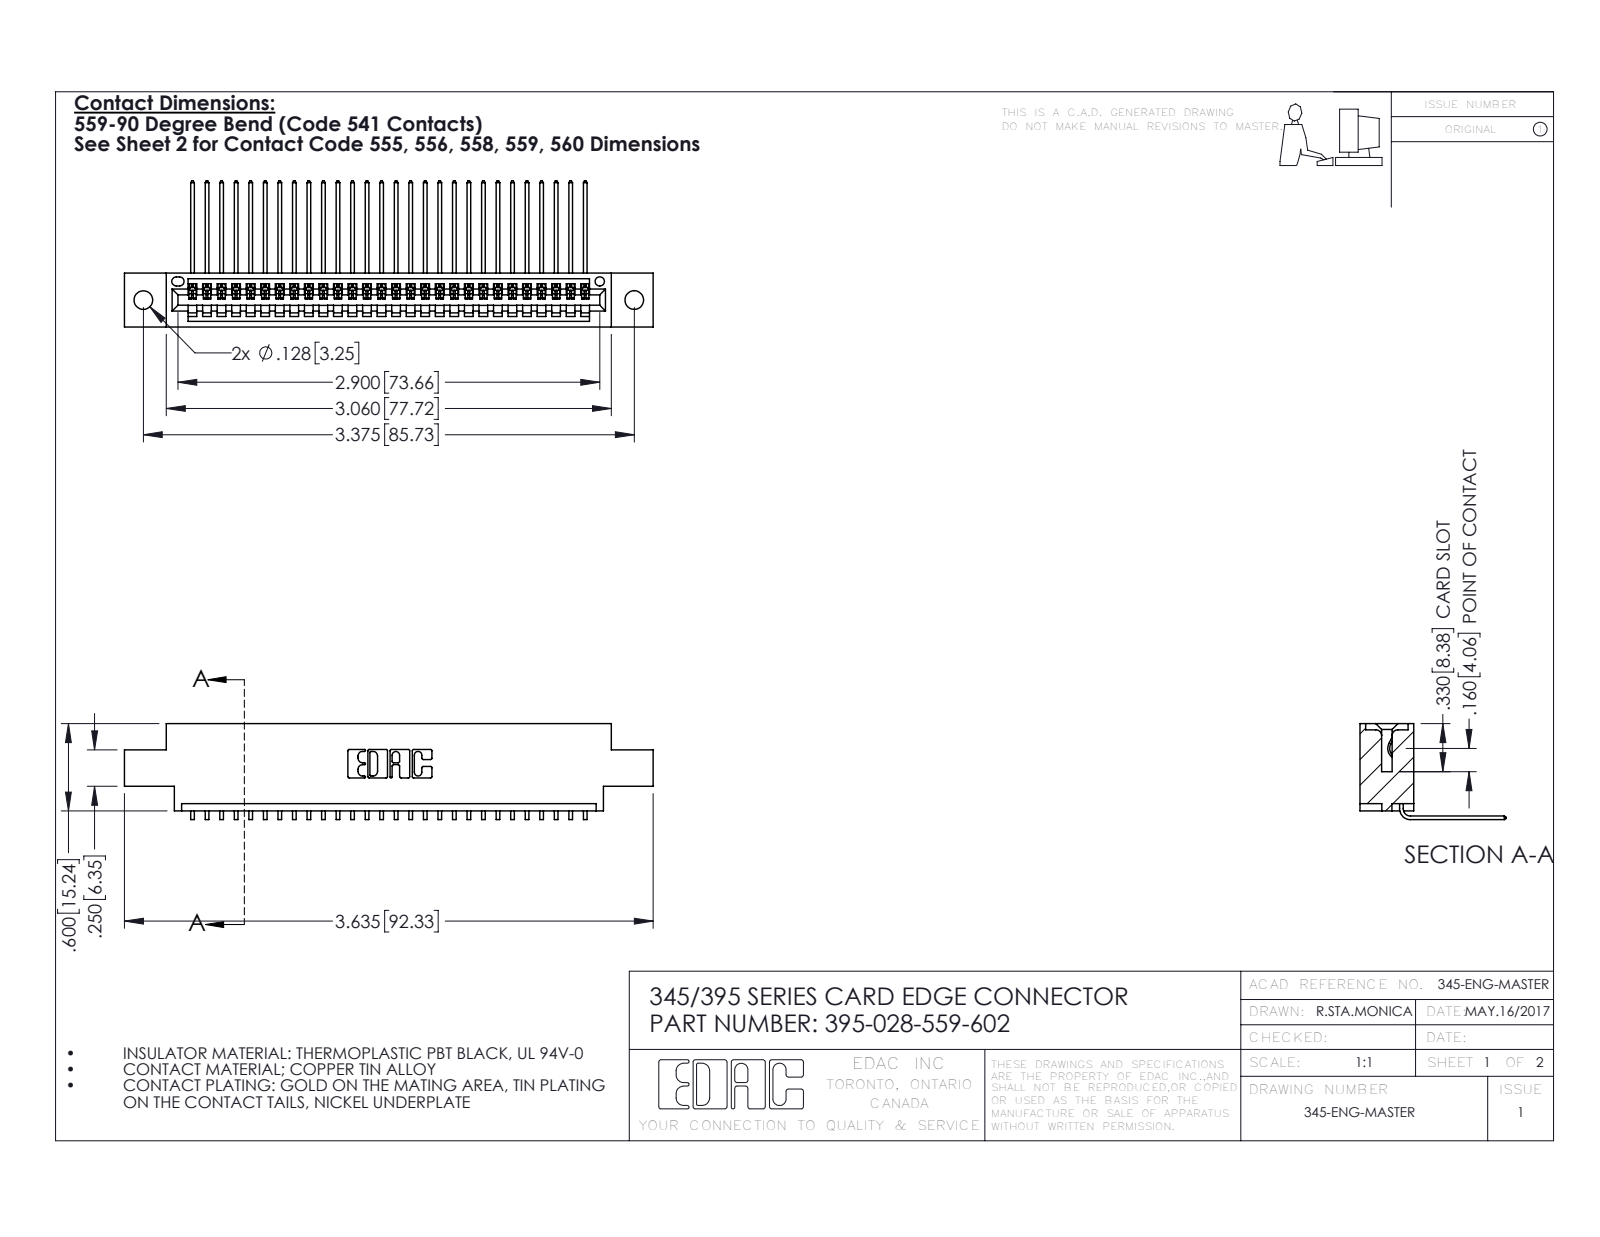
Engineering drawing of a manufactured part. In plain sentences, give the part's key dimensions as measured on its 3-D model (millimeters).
The part is named "395-028-559-602; 345-292-001_558 559 Tail - 1; 345 Part_0.170 Offset - 0.128 Dia". Its 3-D file was written by "SolidWorks 2016 (CONFIG_CONTROL_DESIGN)". It is 29 solids with 1810 faces: 1260 planar, 550 cylindrical and 0 other. Overall it measures 92.3 by 25.5 by 16.7 millimeters. Its volume is 8 600 cubic millimeters and its surface area 11 640 square millimeters. Round holes: 2 of diameter 3.3, 1 of diameter 1.6. Partial cylindrical surfaces (rounded edges, fillets, slot ends): 56 of radius 0.2, 22 of radius 0.3, 6 of radius 0.2, 6 of radius 0.8, 3 of radius 0.7, 2 of radius 0.8, 2 of radius 1, 1 of radius 0.4. The main face-to-face distances are 1.8, 7.6, 9.4, 5.1, 2.5, 6.9, 0.6, 5.7, 4.4, 3.8. The hole center spacings are 6.9, 79.8, 85.7.
